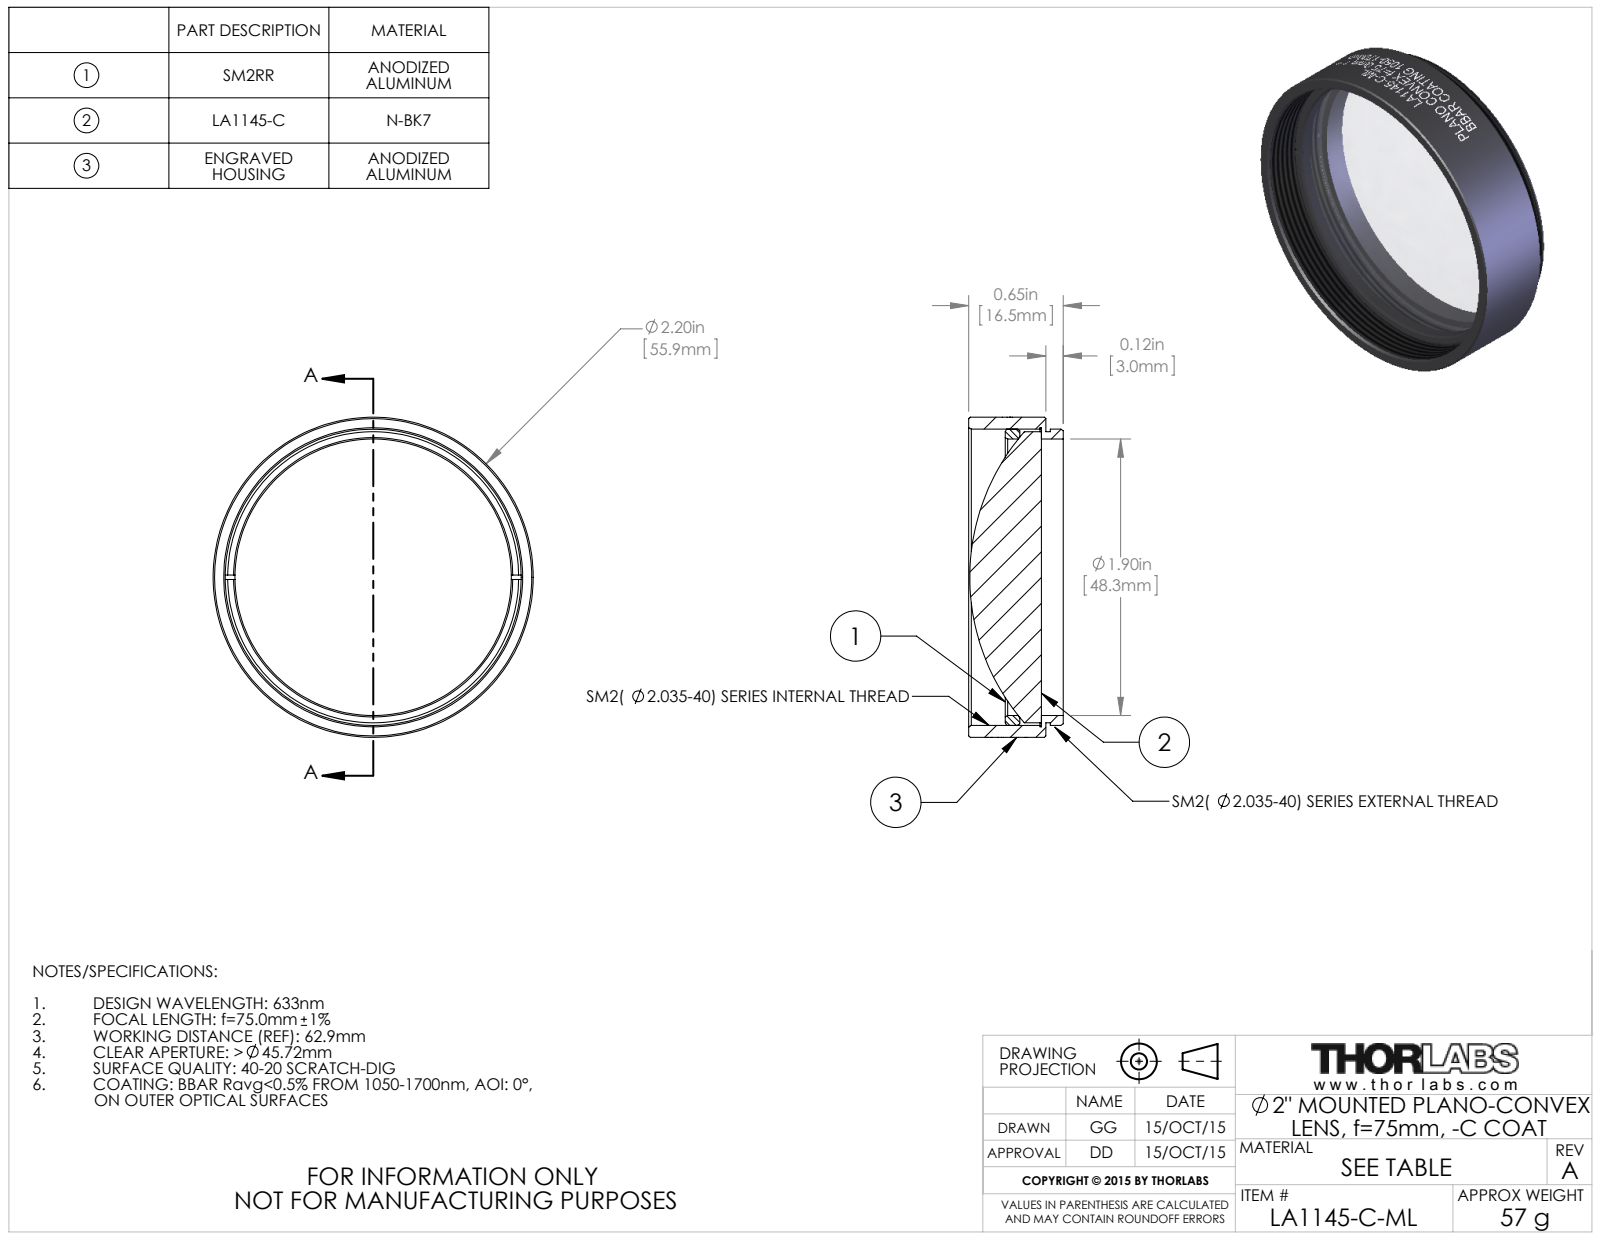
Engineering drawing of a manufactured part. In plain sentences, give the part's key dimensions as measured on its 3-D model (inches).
The part is named "TTN039517-E0W". Its 3-D file was written by "SolidWorks 2014 (CONFIG_CONTROL_DESIGN)". It is 3 solids with 147 faces: 16 planar, 107 cylindrical and 24 other. Overall it measures 2.2 by 2.2 by 0.65 inches. Its volume is 1.374 cubic inches and its surface area 19.98 square inches. Round holes: 1 of diameter 1.9, 1 of diameter 2.055. Round bosses or shafts: 1 of diameter 2.2, 1 of diameter 2.035, 1 of diameter 2, 1 of diameter 1.999. The main face-to-face distances are 0.03, 0.5, 0.53, 0.65, 0.15, 0.12, 0.35, 0.15, 0.18, 0.3.
